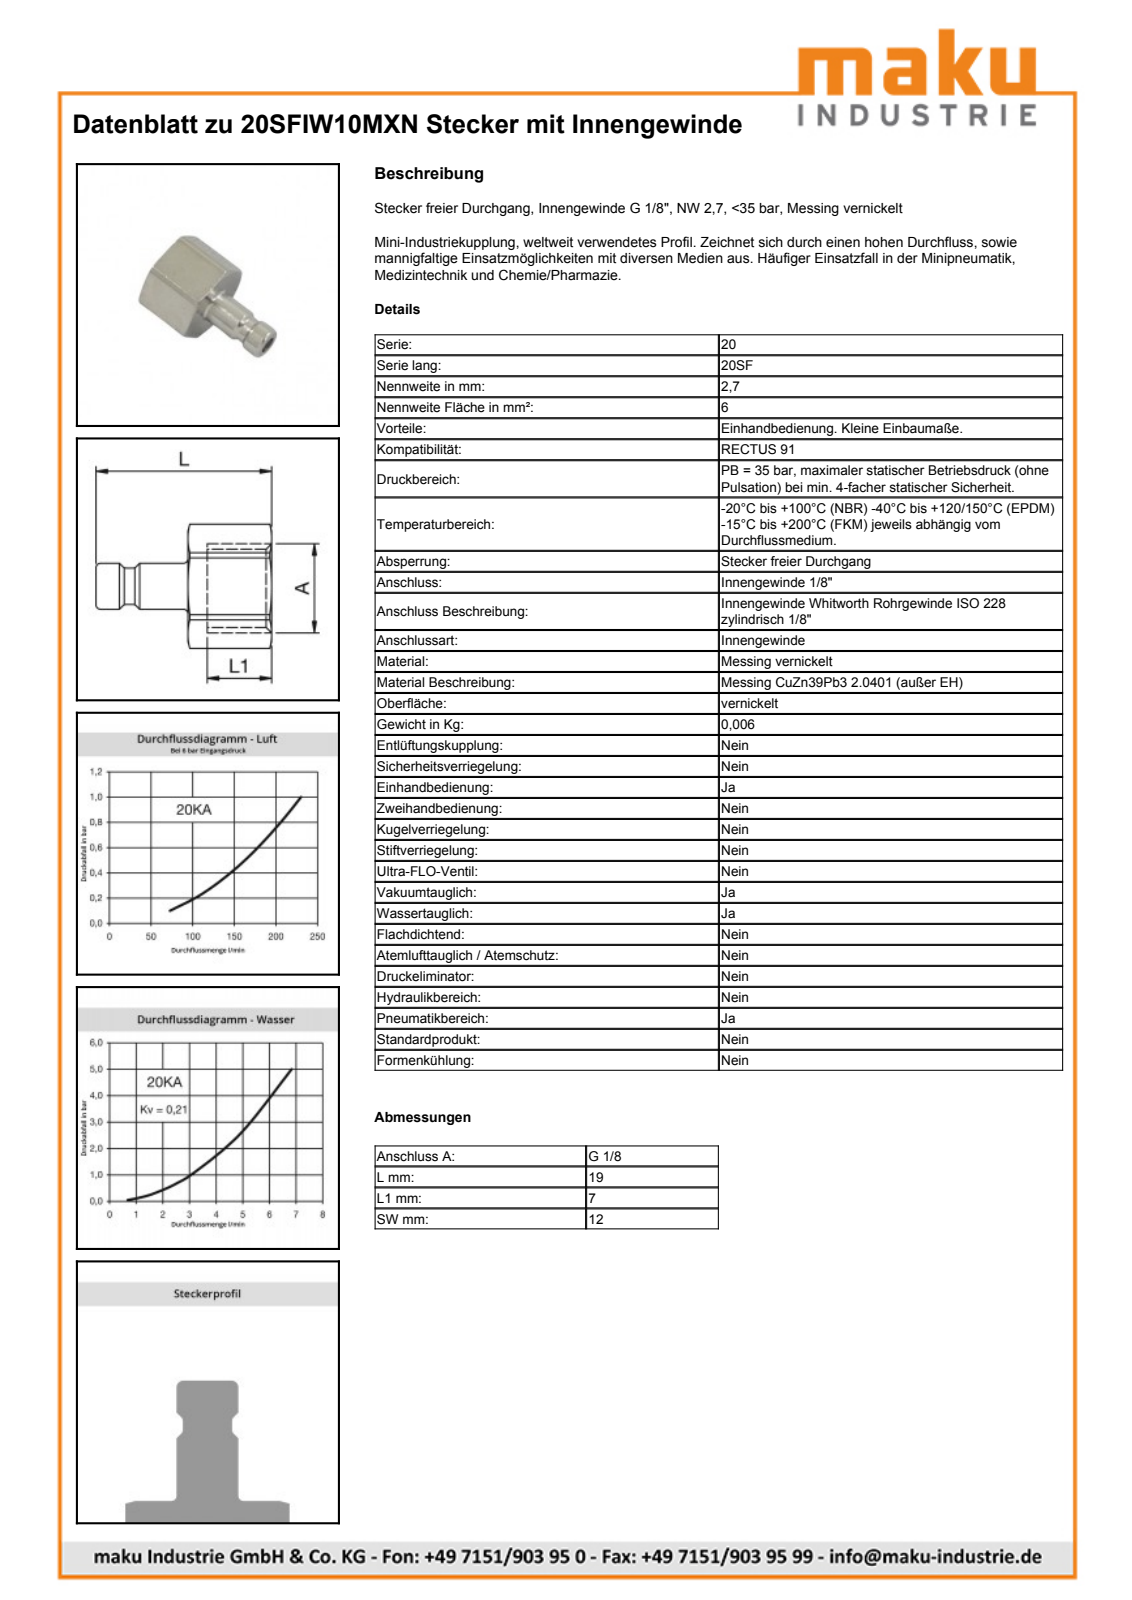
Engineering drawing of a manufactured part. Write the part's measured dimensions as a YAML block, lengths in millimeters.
part_name: "D108539"
step_written_by: "Autodesk Inventor 2013 (AUTOMOTIVE_DESIGN)"
units: millimeters
bodies: {solids: 1, faces: 40, planar: 10, cylindrical: 11, other: 19}
overall_size: [19.1, 13.5, 12]
volume: 836
surface_area: 1037
round_holes:
  - {diameter: 2.7, count: 1}
  - {diameter: 8.57, count: 1}
round_bosses_or_shafts:
  - {diameter: 5, count: 1}
  - {diameter: 3.95, count: 1}
partial_cylinders:
  - {radius: 6.75, count: 1}
face_to_face_distances: [12, 2.1, 9.1, 7, 10, 12.1, 19.1]
